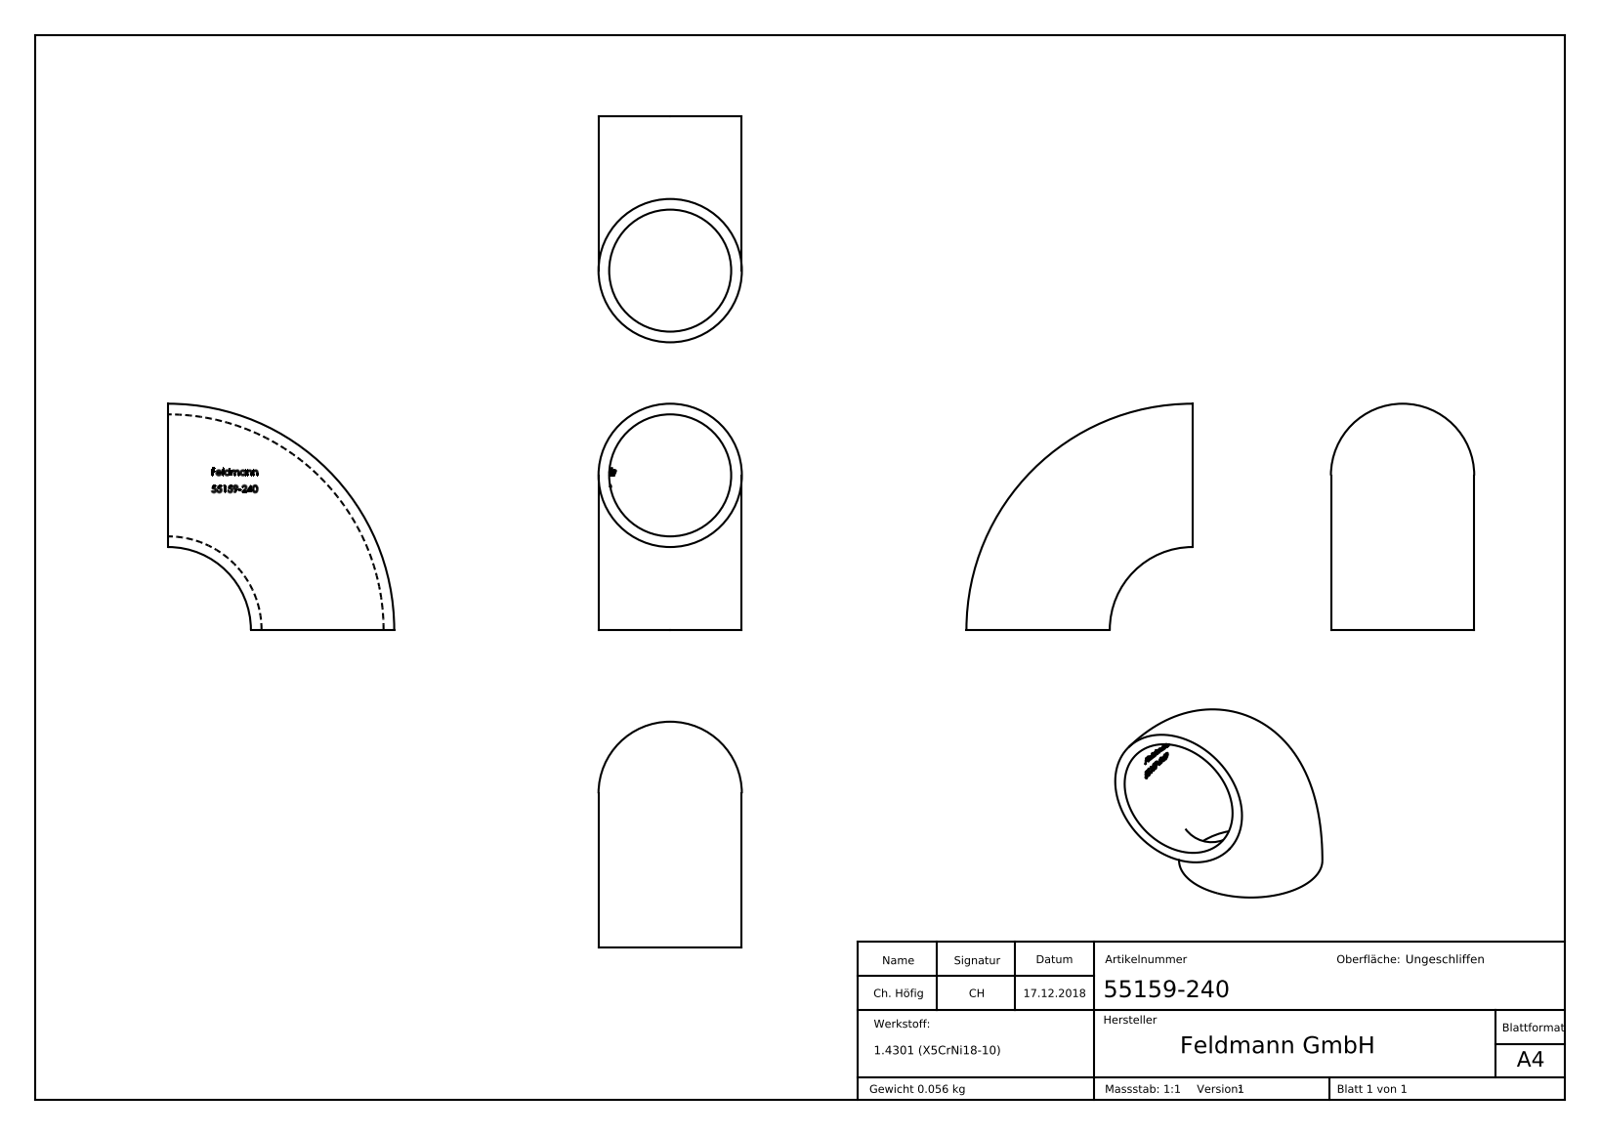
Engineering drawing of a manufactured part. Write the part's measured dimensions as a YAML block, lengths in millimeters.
part_name: "55159-240"
step_written_by: "SolidWorks 2015 (CONFIG_CONTROL_DESIGN)"
units: millimeters
bodies: {solids: 1, faces: 229, planar: 106, cylindrical: 0, other: 123}
overall_size: [42.45, 42.45, 26.9]
volume: 7126
surface_area: 7449
face_to_face_distances: [0.39, 1.26, 2.97, 1.32, 4.23, 2.02, 3.66, 3.27, 2.4, 0.88]
